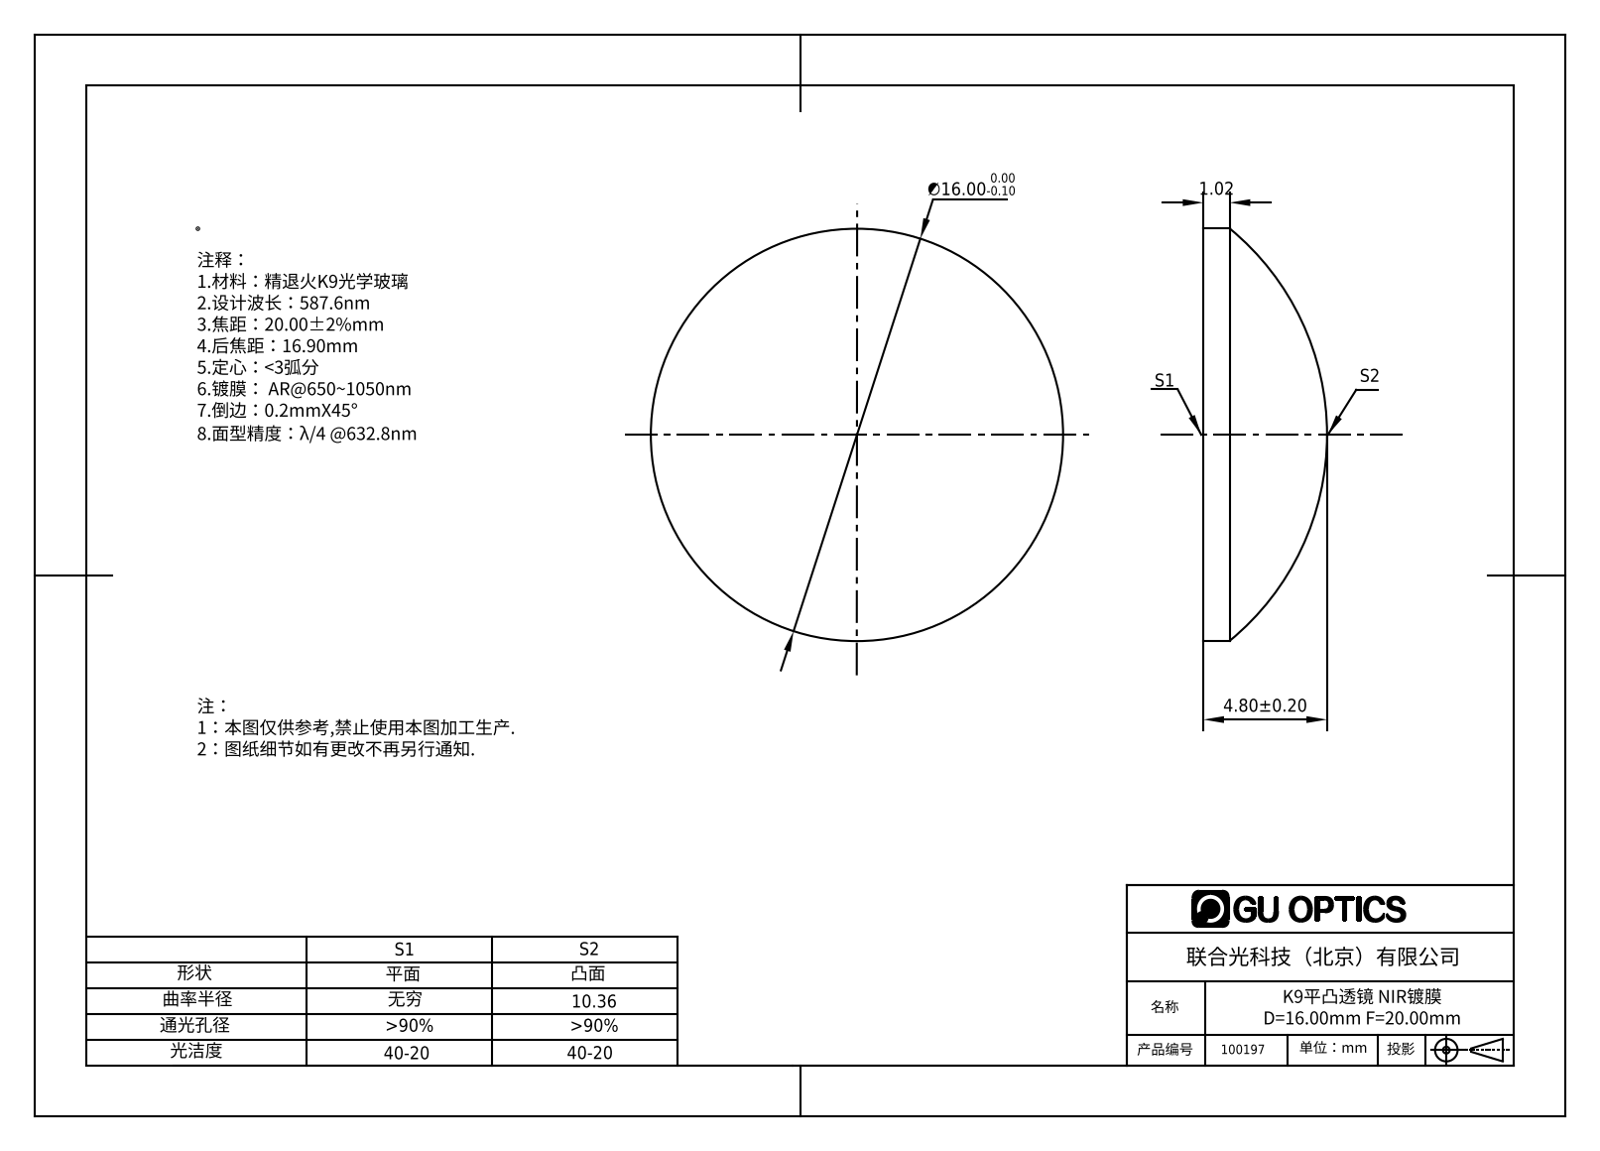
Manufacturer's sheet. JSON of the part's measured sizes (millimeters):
{"part_name": "100197", "step_written_by": "SolidWorks 2016 (AUTOMOTIVE_DESIGN)", "units": "millimeters", "bodies": {"solids": 1, "faces": 5, "planar": 1, "cylindrical": 2, "other": 2}, "overall_size": [16, 16, 4.8], "volume_mm3": 613, "surface_area_mm2": 498, "round_bosses_or_shafts": [[16, 1]]}
